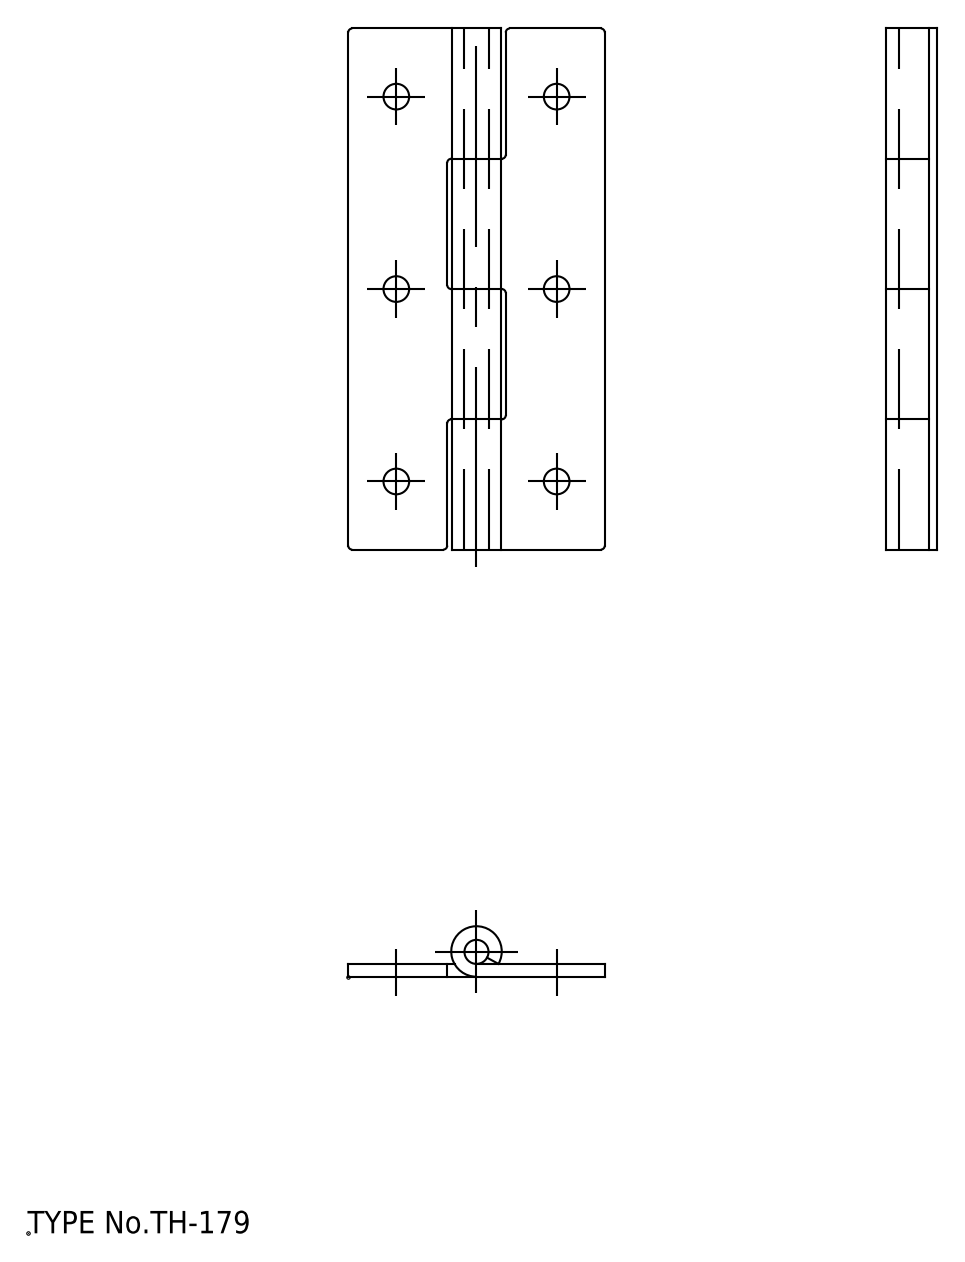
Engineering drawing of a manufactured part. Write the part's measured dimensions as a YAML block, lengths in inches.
step_written_by: "spGate 17.5.2 (AUTOMOTIVE_DESIGN)"
units: inches
bodies: {solids: 3, faces: 60, planar: 26, cylindrical: 34, other: 0}
overall_size: [2.559, 1.26, 0.248]
volume: 0.283
surface_area: 10.22
round_holes:
  - {diameter: 0.126, count: 6}
  - {diameter: 0.118, count: 1}
round_bosses_or_shafts:
  - {diameter: 0.248, count: 1}
partial_cylinders:
  - {radius: 0.02, count: 12}
face_to_face_distances: [0.063, 0.64, 1.28, 1.26, 1.919, 0.486, 0.774, 2.559, 0.287]
hole_center_spacings: [0.945, 1.23, 0.787, 1.89, 2.047]
